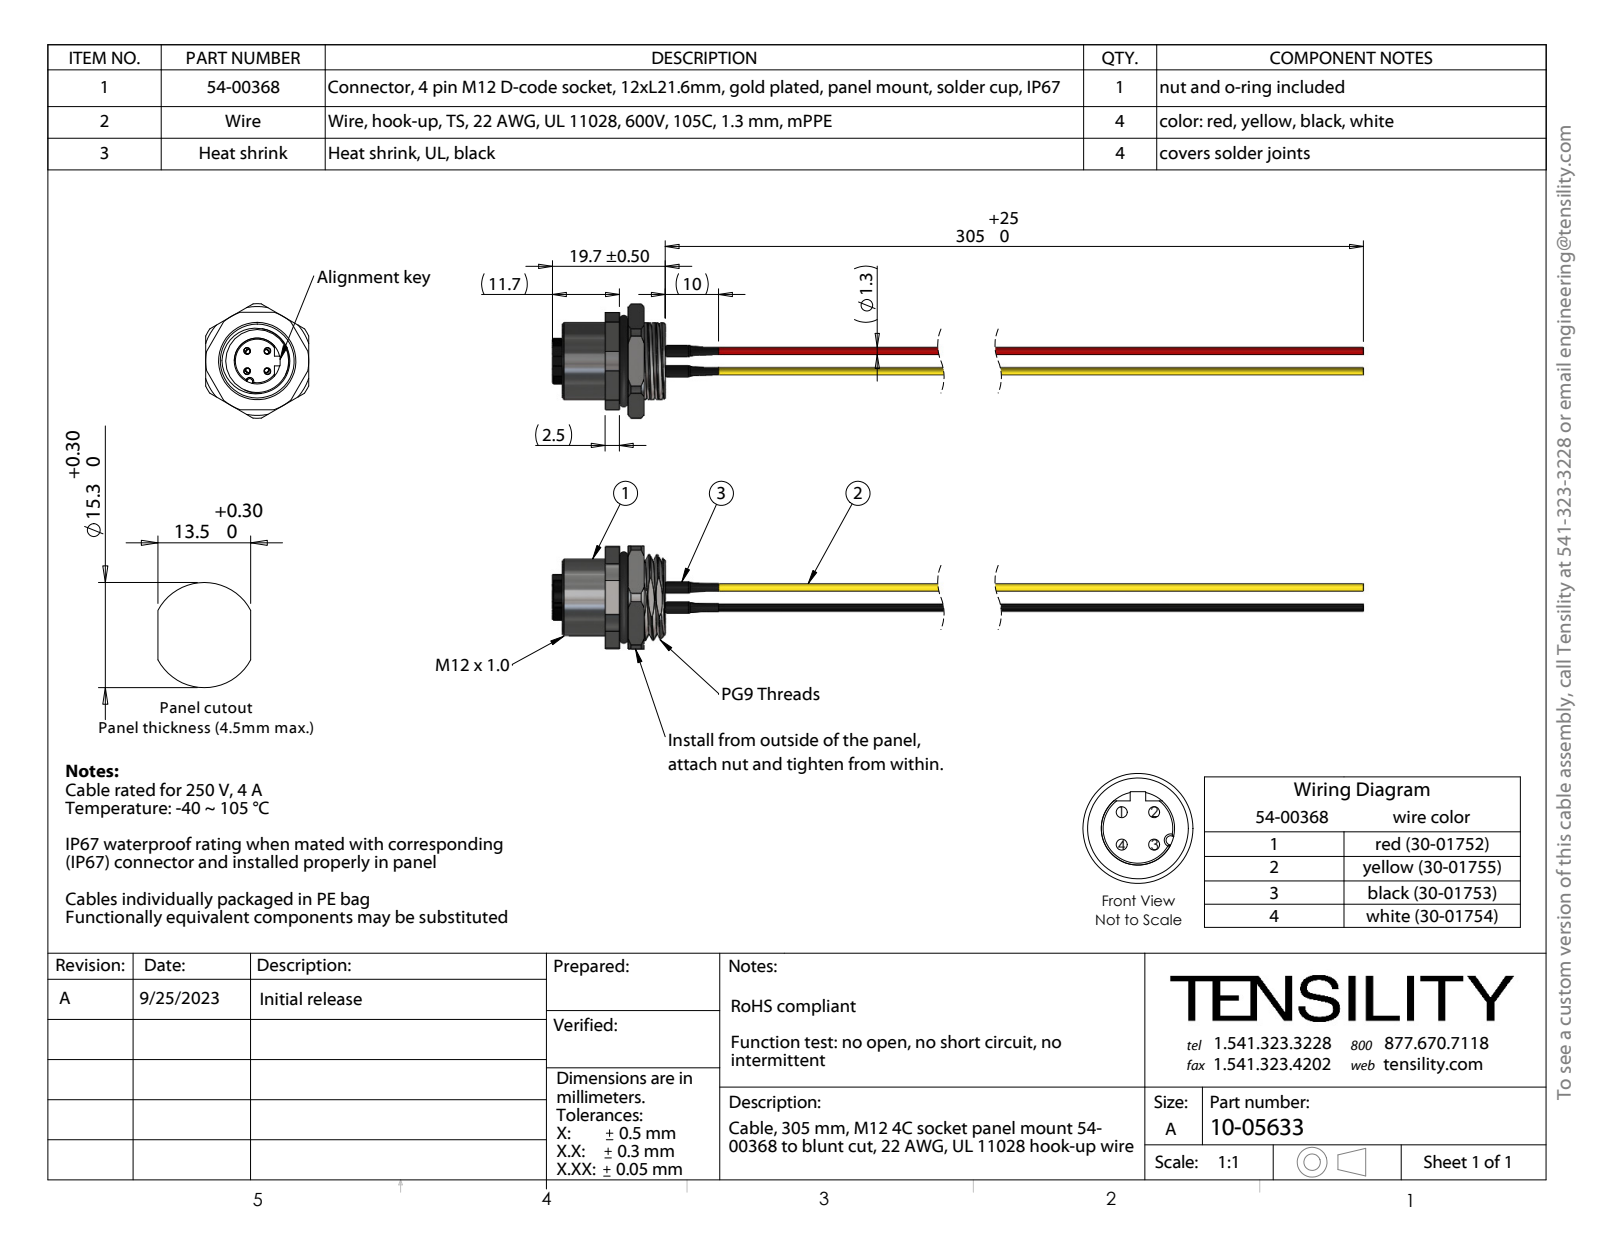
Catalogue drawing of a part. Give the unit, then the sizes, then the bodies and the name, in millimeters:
Units: millimetres
Overall size (bounding box): 169 × 20 × 18
Round holes (diameter × count): ⌀1.1 ×4, ⌀1.2 ×4, ⌀9 ×1, ⌀11 ×1, ⌀14 ×1
Round bosses / shafts (diameter × count): ⌀2 ×4, ⌀1.6 ×4, ⌀1.5 ×4, ⌀1.3 ×4, ⌀13.5 ×1, ⌀13 ×1, ⌀12 ×1, ⌀10.6 ×1
Partial cylindrical surfaces — rounded edges, fillets, slot ends (radius × count): R0.1 ×8, R0.4 ×7, R0.2 ×2, R0.5 ×1, R4 ×1, R7.5 ×1, R9 ×1, R10 ×1
Main face-to-face distances: 3, 7.3, 2.5, 2, 1.5, 5.3, 5, 9.8, 2.3, 18
Hole centre spacings: 0.48, 0.31, 0.32, 3.54, 0.37, 5, 0.45, 0.53
Volume: 3 681 mm³ · Surface area: 18 192 mm²
Bodies: 85 solids, 993 faces (309 planar, 481 cylindrical, 203 other)
Part name (STEP PRODUCT): 30-01752_blunt cut; 54-00368-06; 54-00368-02; 54-00368 (+8 more)
STEP written by: SolidWorks 2021 (AUTOMOTIVE_DESIGN)
